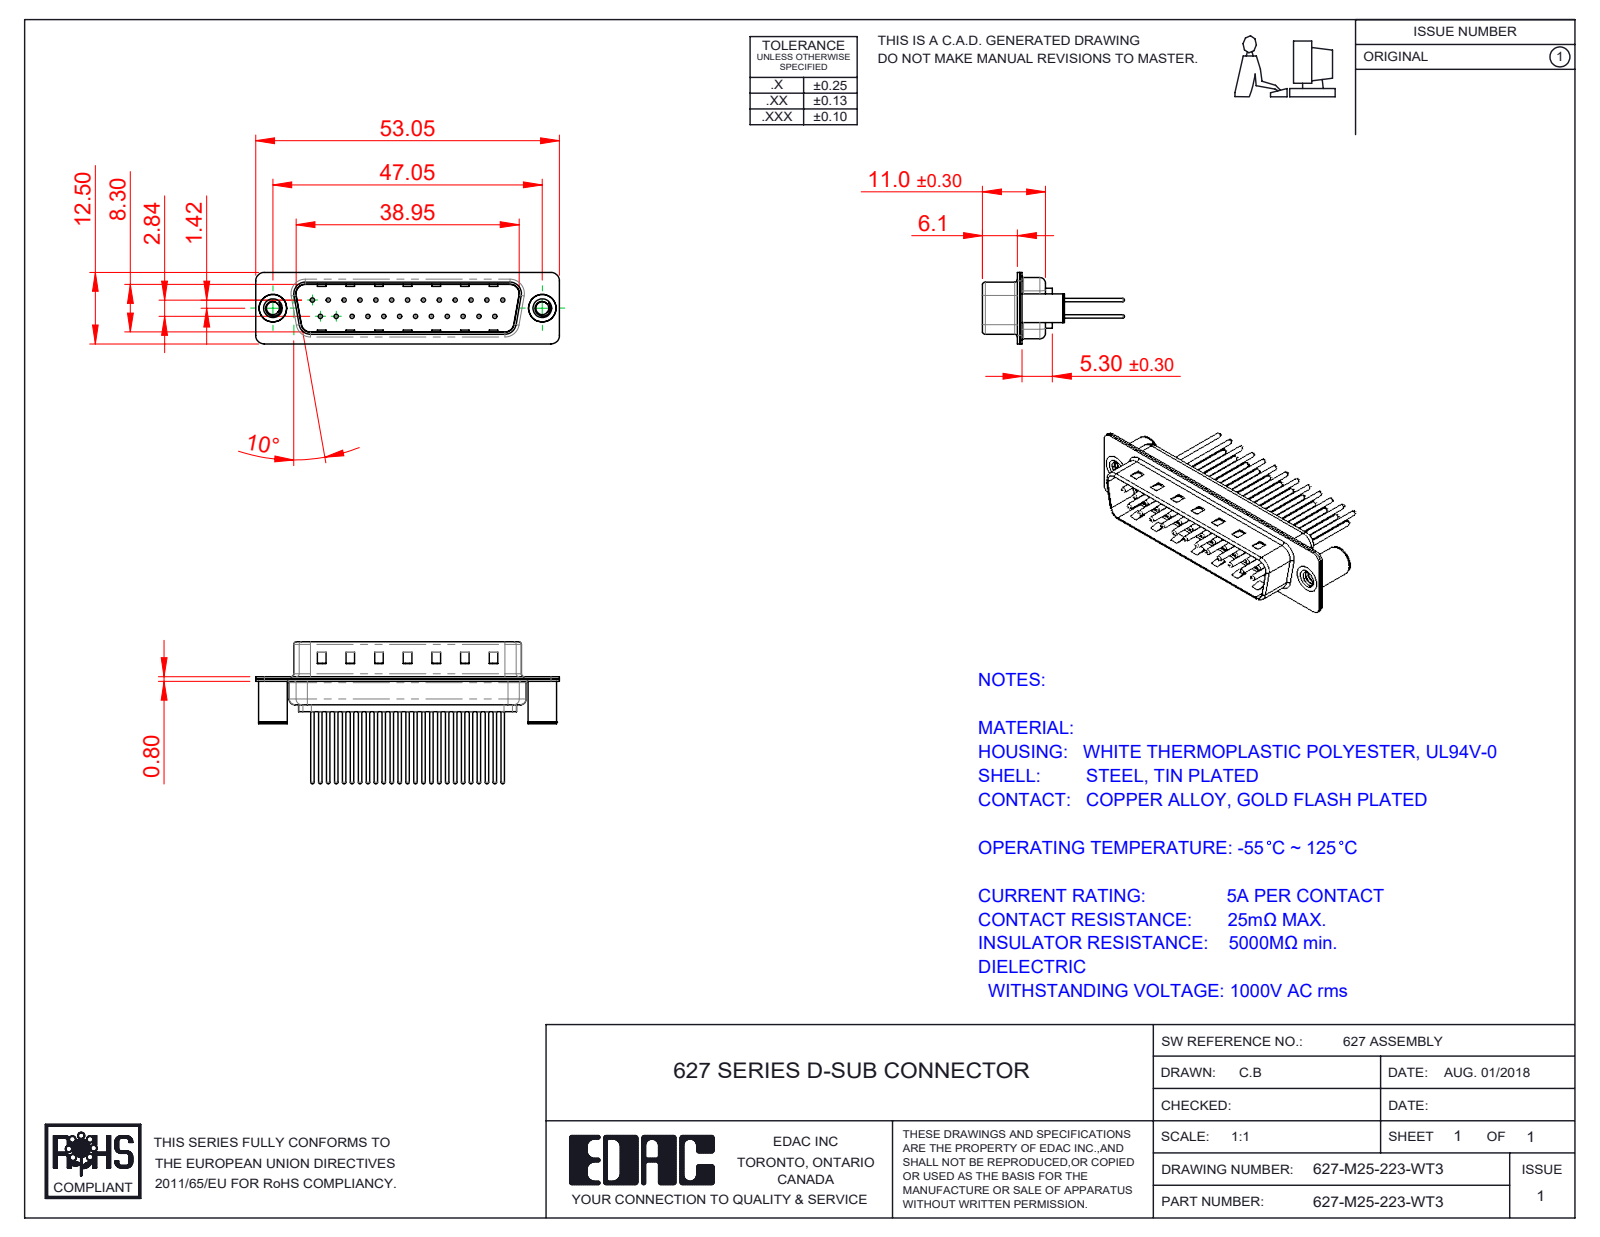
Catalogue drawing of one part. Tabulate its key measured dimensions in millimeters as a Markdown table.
| quantity | value |
| --- | --- |
| part name | 627M Shell Rear_25 Contacts; 627M Shell Front_25 Contacts; 627M Housing_25 Contacts; 627M Contact Row 1_23 (+3 more) |
| STEP written by | SolidWorks 2020 (CONFIG_CONTROL_DESIGN) |
| units | millimeters |
| bodies | 30 solids, 1335 faces (346 planar, 511 cylindrical, 478 other) |
| overall size | 53.05 × 24.77 × 12.5 |
| volume | 2 890 mm³ |
| surface area | 7 425 mm² |
| round holes (diameter × count) | 0.75 × 25, 1.6 × 25, 2 × 25, 2.26 × 2, 3.26 × 2, 4 × 2, 4.8 × 2 |
| round bosses / shafts (diameter × count) | 1.5 × 25, 0.6 × 25, 5 × 2, 4.9 × 2 |
| partial cylindrical surfaces (radius × count) | 1.5 × 16, 2 × 12, 0.5 × 8, 1.6 × 8, 0.25 × 4, 0.6 × 4, 0.65 × 4, 0.9 × 4 |
| main face-to-face distances | 0.4, 0.8, 9.5, 9.1, 8.7, 9.9, 1.2, 6.1, 5.7, 0.75 |
| hole center spacings | 3.16, 2.77, 5.54, 8.31, 11.08, 13.85, 16.62, 5.03 |
